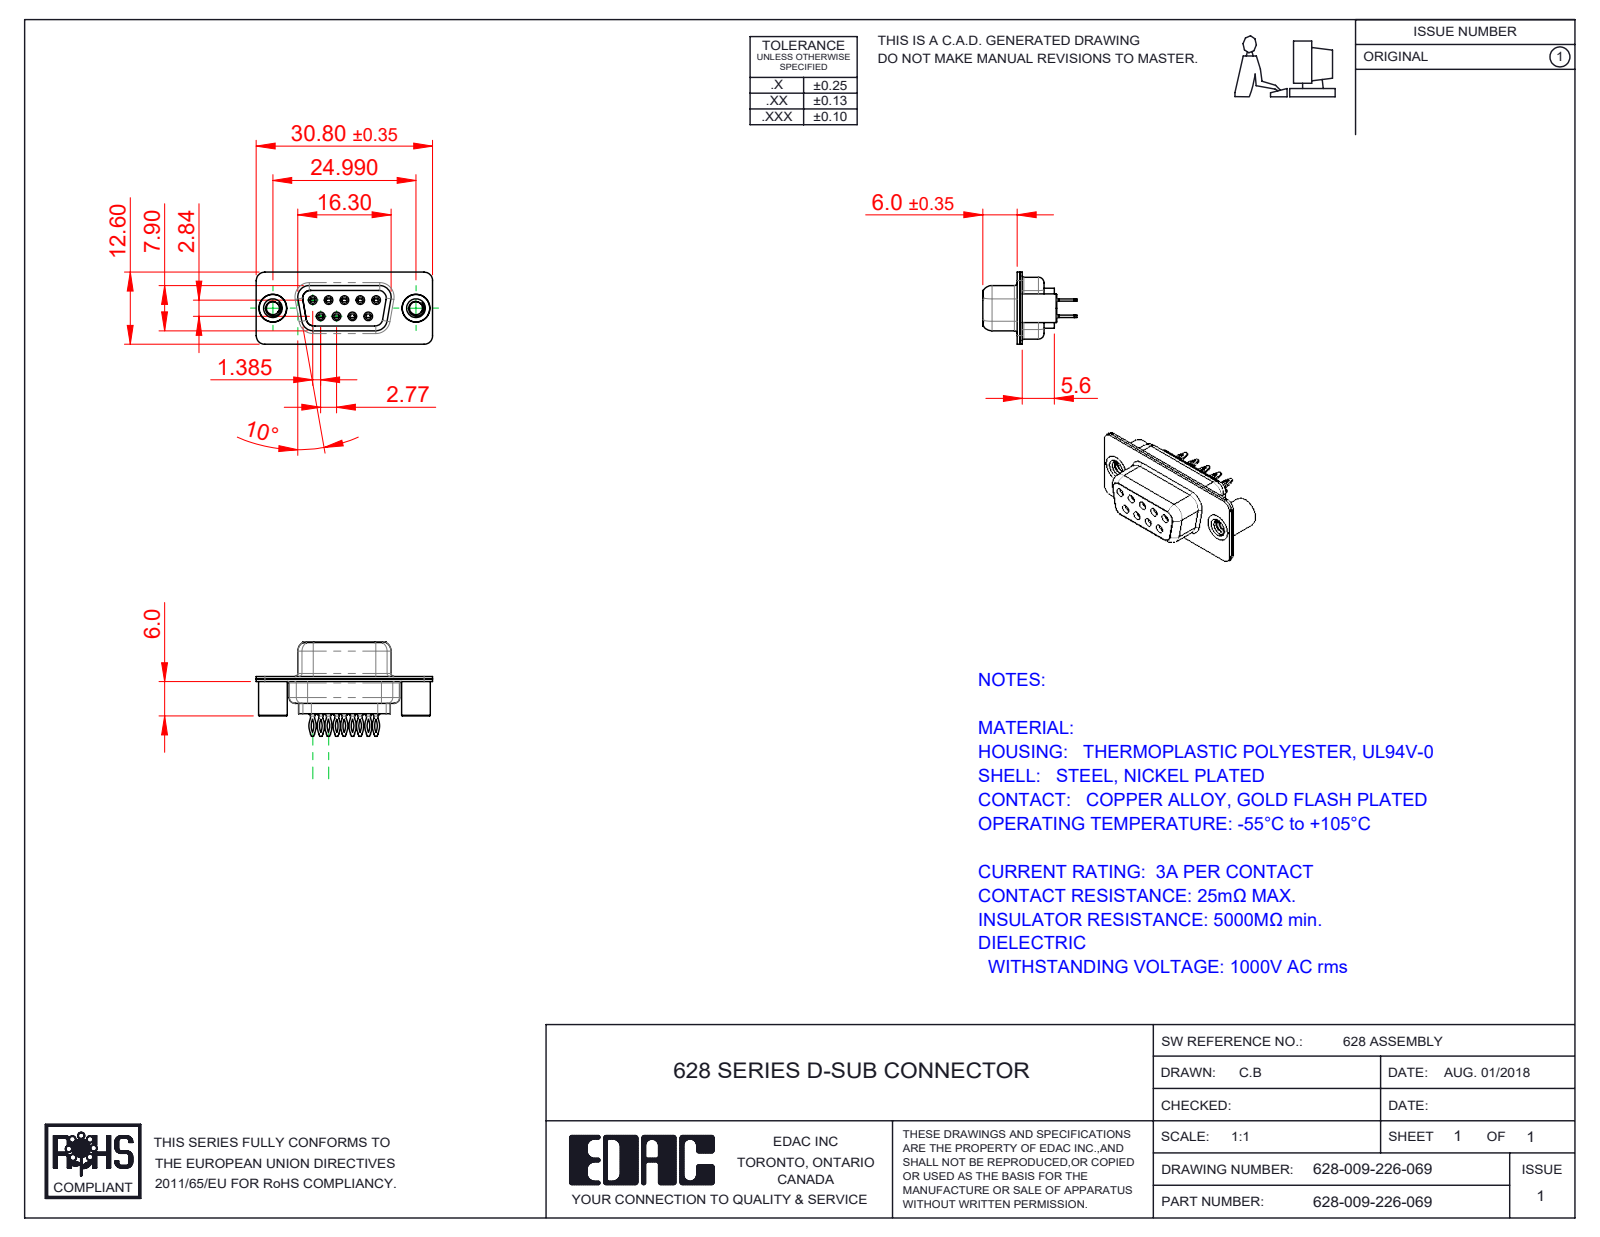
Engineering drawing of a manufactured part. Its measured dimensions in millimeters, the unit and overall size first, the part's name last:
Units: millimetres
Overall size (bounding box): 30.8 × 16.45 × 12.6
Round holes (diameter × count): ⌀0.8 ×9, ⌀0.9 ×9, ⌀1.1 ×9, ⌀1.6 ×9, ⌀1.7 ×5, ⌀2.26 ×2, ⌀4 ×2, ⌀4.05 ×2, ⌀4.85 ×2
Round bosses / shafts (diameter × count): ⌀2 ×9, ⌀1.5 ×9, ⌀1.2 ×9, ⌀5 ×2, ⌀4.95 ×2, ⌀4.8 ×2
Partial cylindrical surfaces — rounded edges, fillets, slot ends (radius × count): R2.92 ×18, R3.33 ×18, R1.5 ×17, R2 ×12, R0.28 ×9, R1.35 ×6, R0.25 ×4, R0.5 ×4
Main face-to-face distances: 0.45, 0.4, 0.9, 1.9, 8.5, 6.6, 1.4, 6.5, 0.5, 6
Hole centre spacings: 3.16, 2.77, 5.54, 5.03, 5.04, 8.31, 7.48, 7.49
Volume: 1 854 mm³ · Surface area: 4 668 mm²
Bodies: 14 solids, 1210 faces (310 planar, 400 cylindrical, 500 other)
Part name (STEP PRODUCT): 628 Contact Row 2_26L; 628 Contact Row 1_26L; 628 Shell Rear_09 Contacts; 628-009-226-069 (+3 more)
STEP written by: SolidWorks 2020 (CONFIG_CONTROL_DESIGN)
